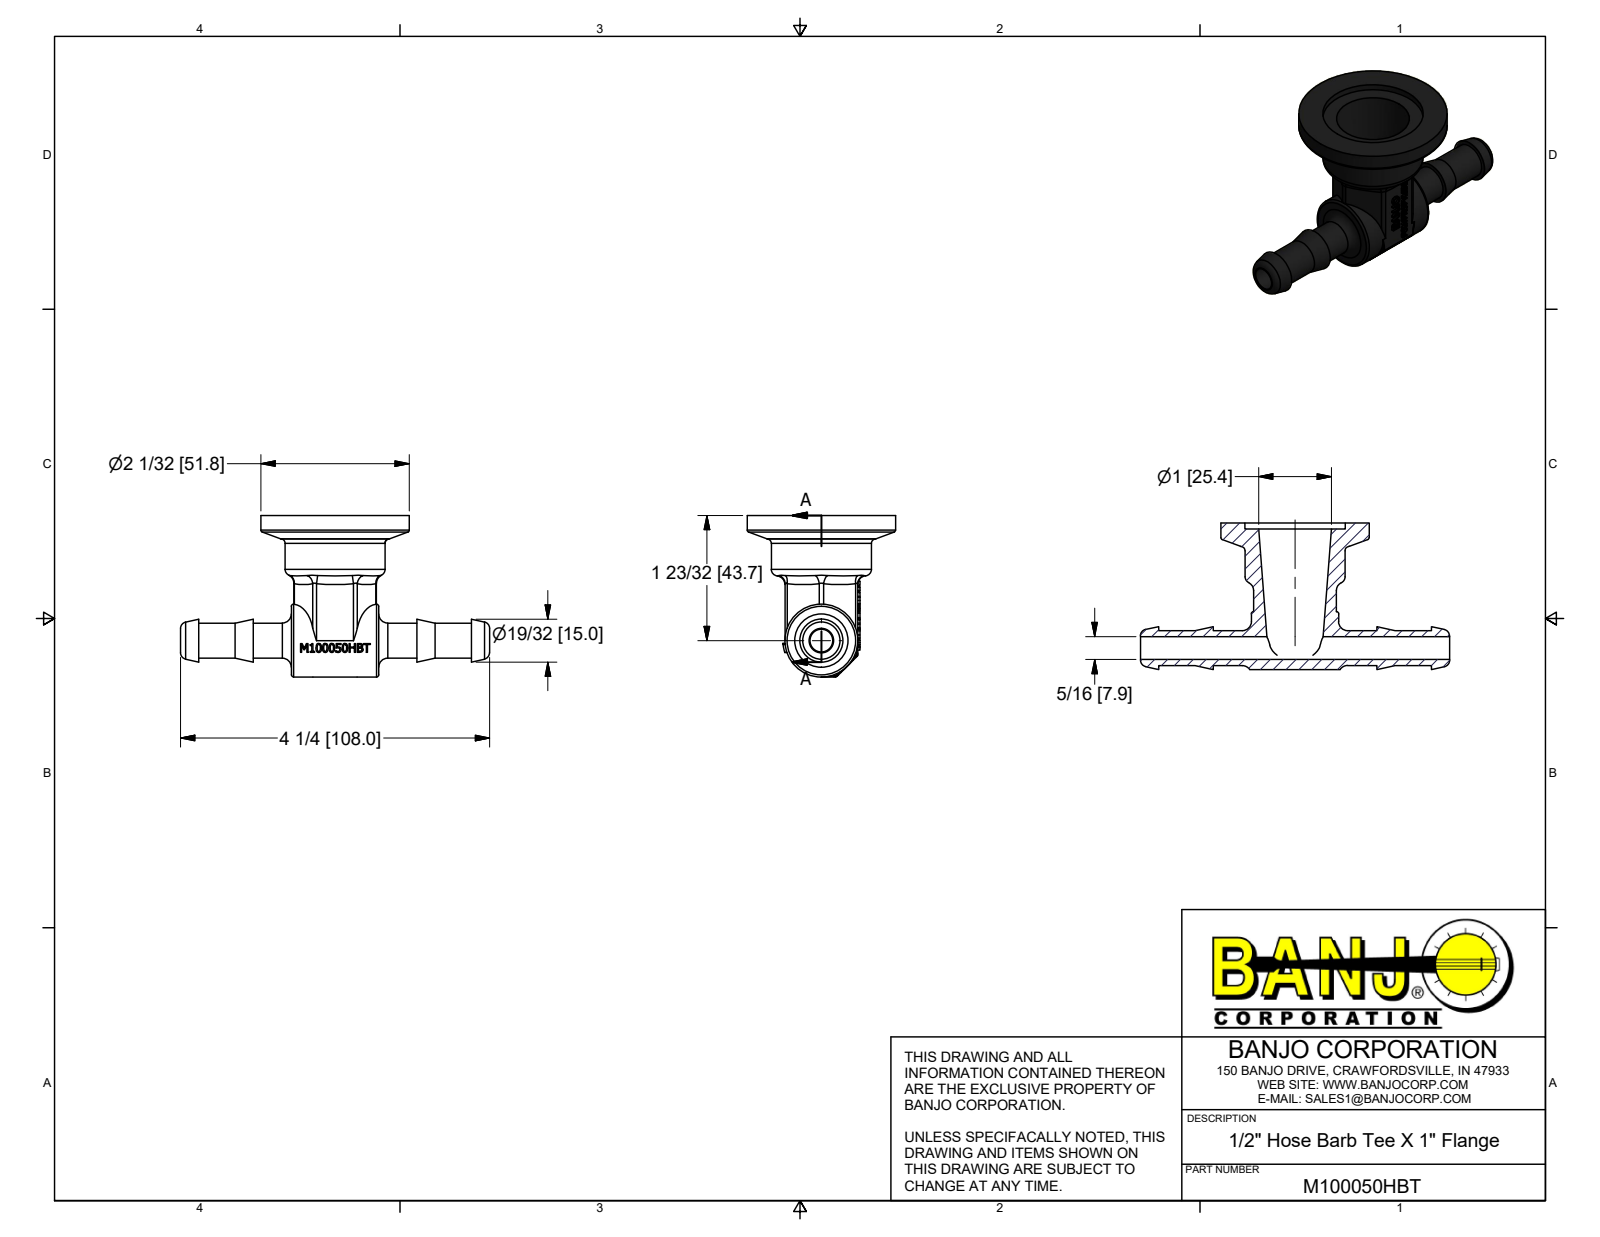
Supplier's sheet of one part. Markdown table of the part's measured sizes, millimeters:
| quantity | value |
| --- | --- |
| part name | M100050HBTU |
| STEP written by | Autodesk Inventor 2017 (AUTOMOTIVE_DESIGN) |
| units | millimeters |
| bodies | 1 solid, 515 faces (246 planar, 42 cylindrical, 227 other) |
| overall size | 107.95 × 56.39 × 51.82 |
| volume | 37 207 mm³ |
| surface area | 18 284 mm² |
| round holes (diameter × count) | 7.94 × 1, 35.05 × 1 |
| round bosses / shafts (diameter × count) | 51.82 × 1, 34.92 × 1, 25.4 × 1, 12.19 × 1 |
| partial cylindrical surfaces (radius × count) | 0.38 × 6, 1.52 × 6, 0.76 × 2, 13.46 × 1 |
| main face-to-face distances | 25.4, 2.14, 30.48, 19.05, 32.38, 62.86, 13.33, 43.81, 76.19, 54.25 |
